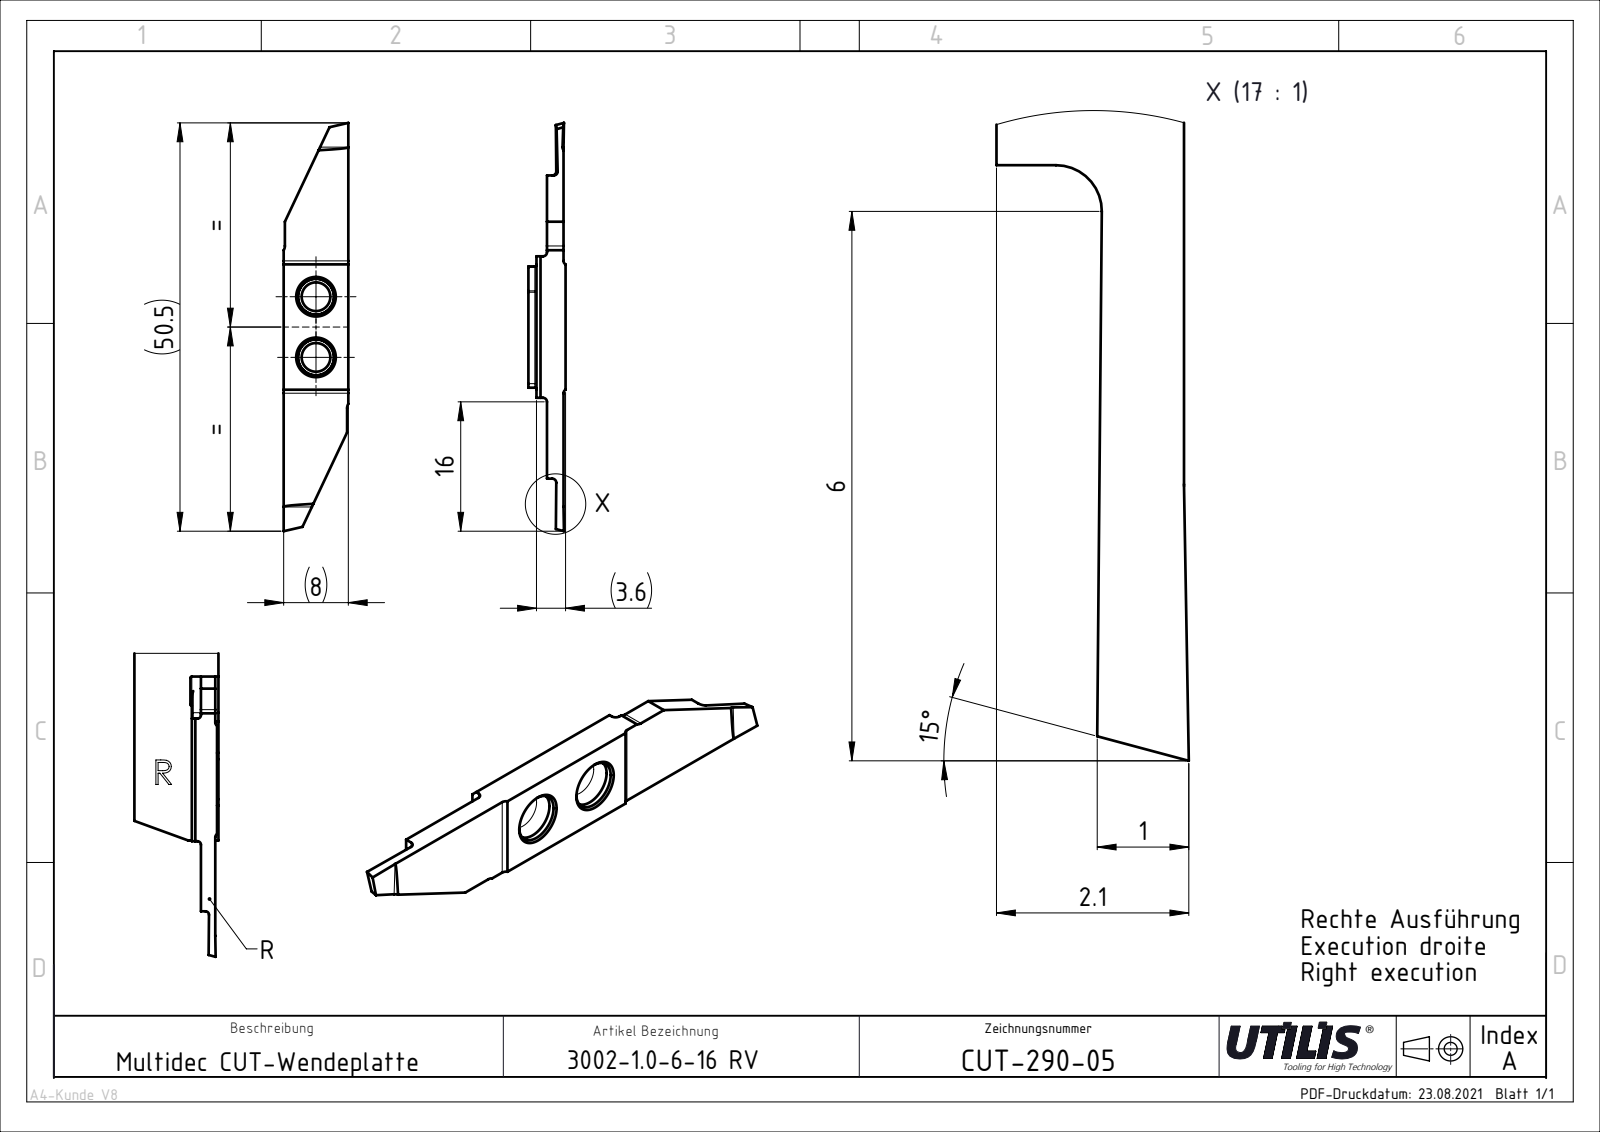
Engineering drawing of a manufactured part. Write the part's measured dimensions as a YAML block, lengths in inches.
part_name: "CUT-290-05"
step_written_by: "SolidWorks 2016 (AUTOMOTIVE_DESIGN)"
units: inches
bodies: {solids: 1, faces: 38, planar: 24, cylindrical: 14, other: 0}
overall_size: [1.988, 0.315, 0.14]
volume: 0.046
surface_area: 1.48
round_holes:
  - {diameter: 0.14, count: 2}
partial_cylinders:
  - {radius: 0.02, count: 6}
  - {radius: 0.006, count: 2}
  - {radius: 0.039, count: 2}
face_to_face_distances: [0.081, 0.049, 0.13, 0.14, 0.091, 0.315, 0.713, 0.309, 0.303, 0.394]
hole_center_spacings: [0.295]
